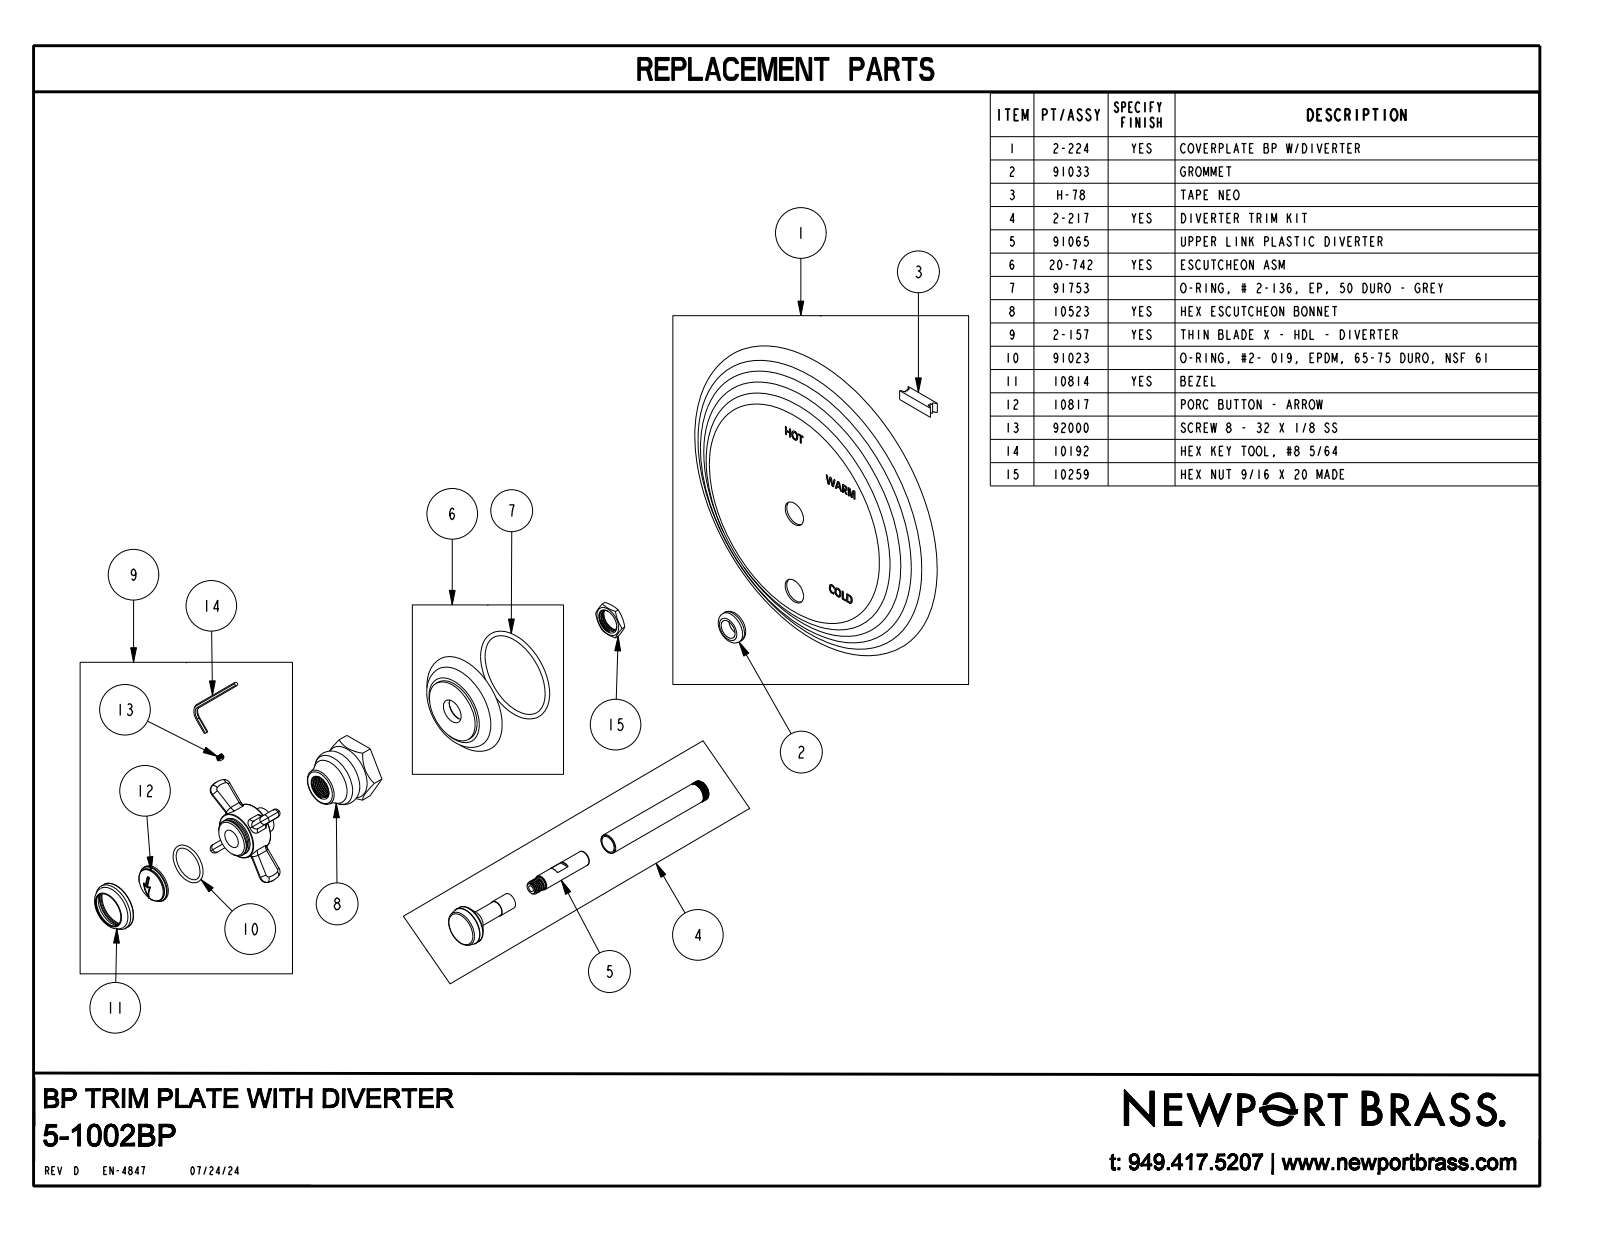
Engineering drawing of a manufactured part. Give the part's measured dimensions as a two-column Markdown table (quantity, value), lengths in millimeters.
| quantity | value |
| --- | --- |
| part name | 5-1002BP |
| STEP written by | CREO PARAMETRIC BY PTC INC, 2018400 (CONFIG_CONTROL_DESIGN) |
| units | millimeters |
| bodies | 1 solid, 365 faces (149 planar, 36 cylindrical, 180 other) |
| overall size | 196.9 × 196.9 × 96.4 |
| volume | 525 500 mm³ |
| surface area | 76 900 mm² |
| round holes (diameter × count) | 20.7 × 1 |
| round bosses / shafts (diameter × count) | 37.6 × 1, 28.3 × 1, 27.9 × 1, 22.9 × 1, 20.3 × 1, 15.3 × 1, 12 × 1, 10.2 × 1 |
| partial cylindrical surfaces (radius × count) | 2.5 × 14 |
| main face-to-face distances | 19.2, 5.1, 71.4, 52.2, 33.4, 58.1, 38.9, 13.3, 62, 42.8 |
